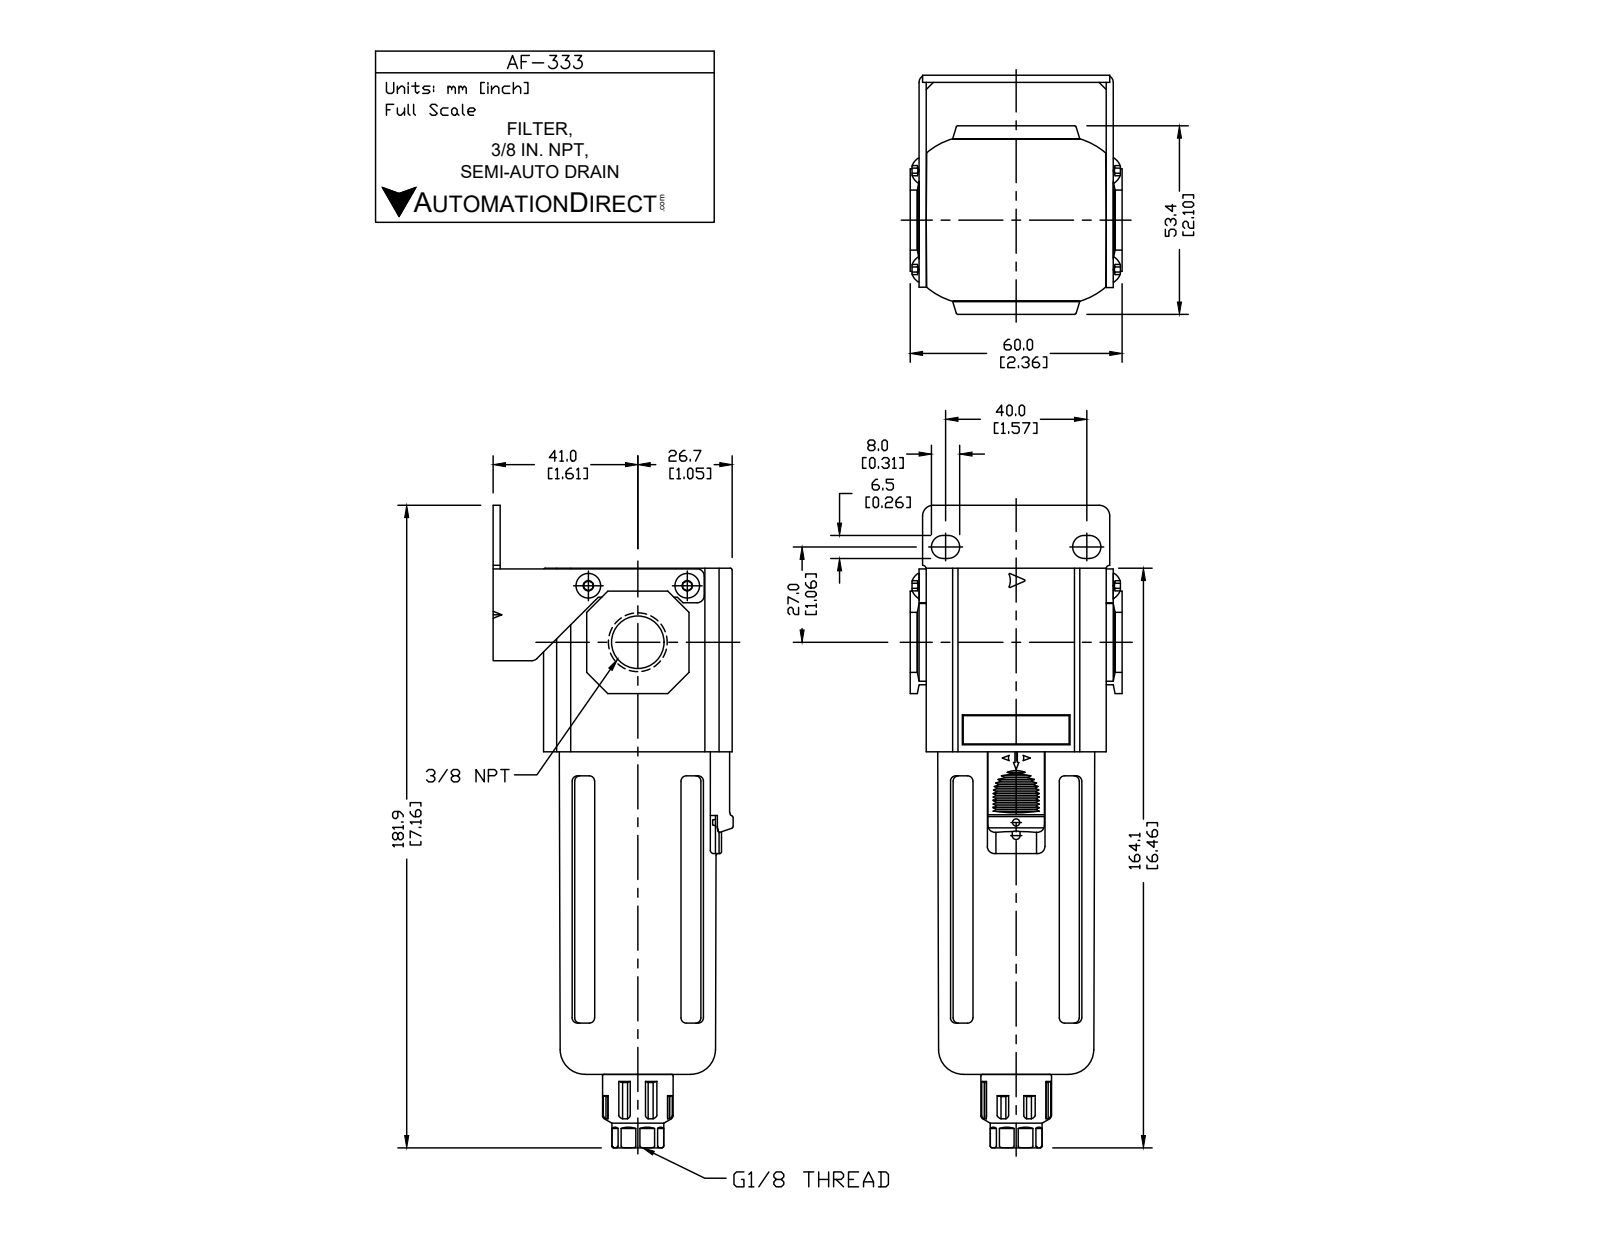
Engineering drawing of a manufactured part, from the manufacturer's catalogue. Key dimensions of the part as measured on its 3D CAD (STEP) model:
Part name (STEP PRODUCT): AF-333
STEP written by: SolidWorks 2015 (CONFIG_CONTROL_DESIGN)
Units: millimetres
Bodies: 9 solids, 394 faces (246 planar, 94 cylindrical, 54 other)
Overall size (bounding box): 182.3 × 67.7 × 60
Volume: 203 276 mm³ · Surface area: 60 945 mm²
Round holes (diameter × count): ⌀3.4 ×2, ⌀8.57 ×1, ⌀14.27 ×1, ⌀35.99 ×1, ⌀44.8 ×1
Round bosses / shafts (diameter × count): ⌀44.47 ×1, ⌀26 ×1, ⌀22.24 ×1, ⌀14.82 ×1
Partial cylindrical surfaces — rounded edges, fillets, slot ends (radius × count): R1 ×18, R2 ×8, R9.5 ×8, R0.5 ×6, R0.3 ×4, R3.25 ×4, R20 ×4, R0.2 ×3
Main face-to-face distances: 2, 51, 53, 2.5, 12.3, 67.7, 65.7, 14.3, 53.4, 55.5
Hole centre spacings: 21.06, 21.46, 28
